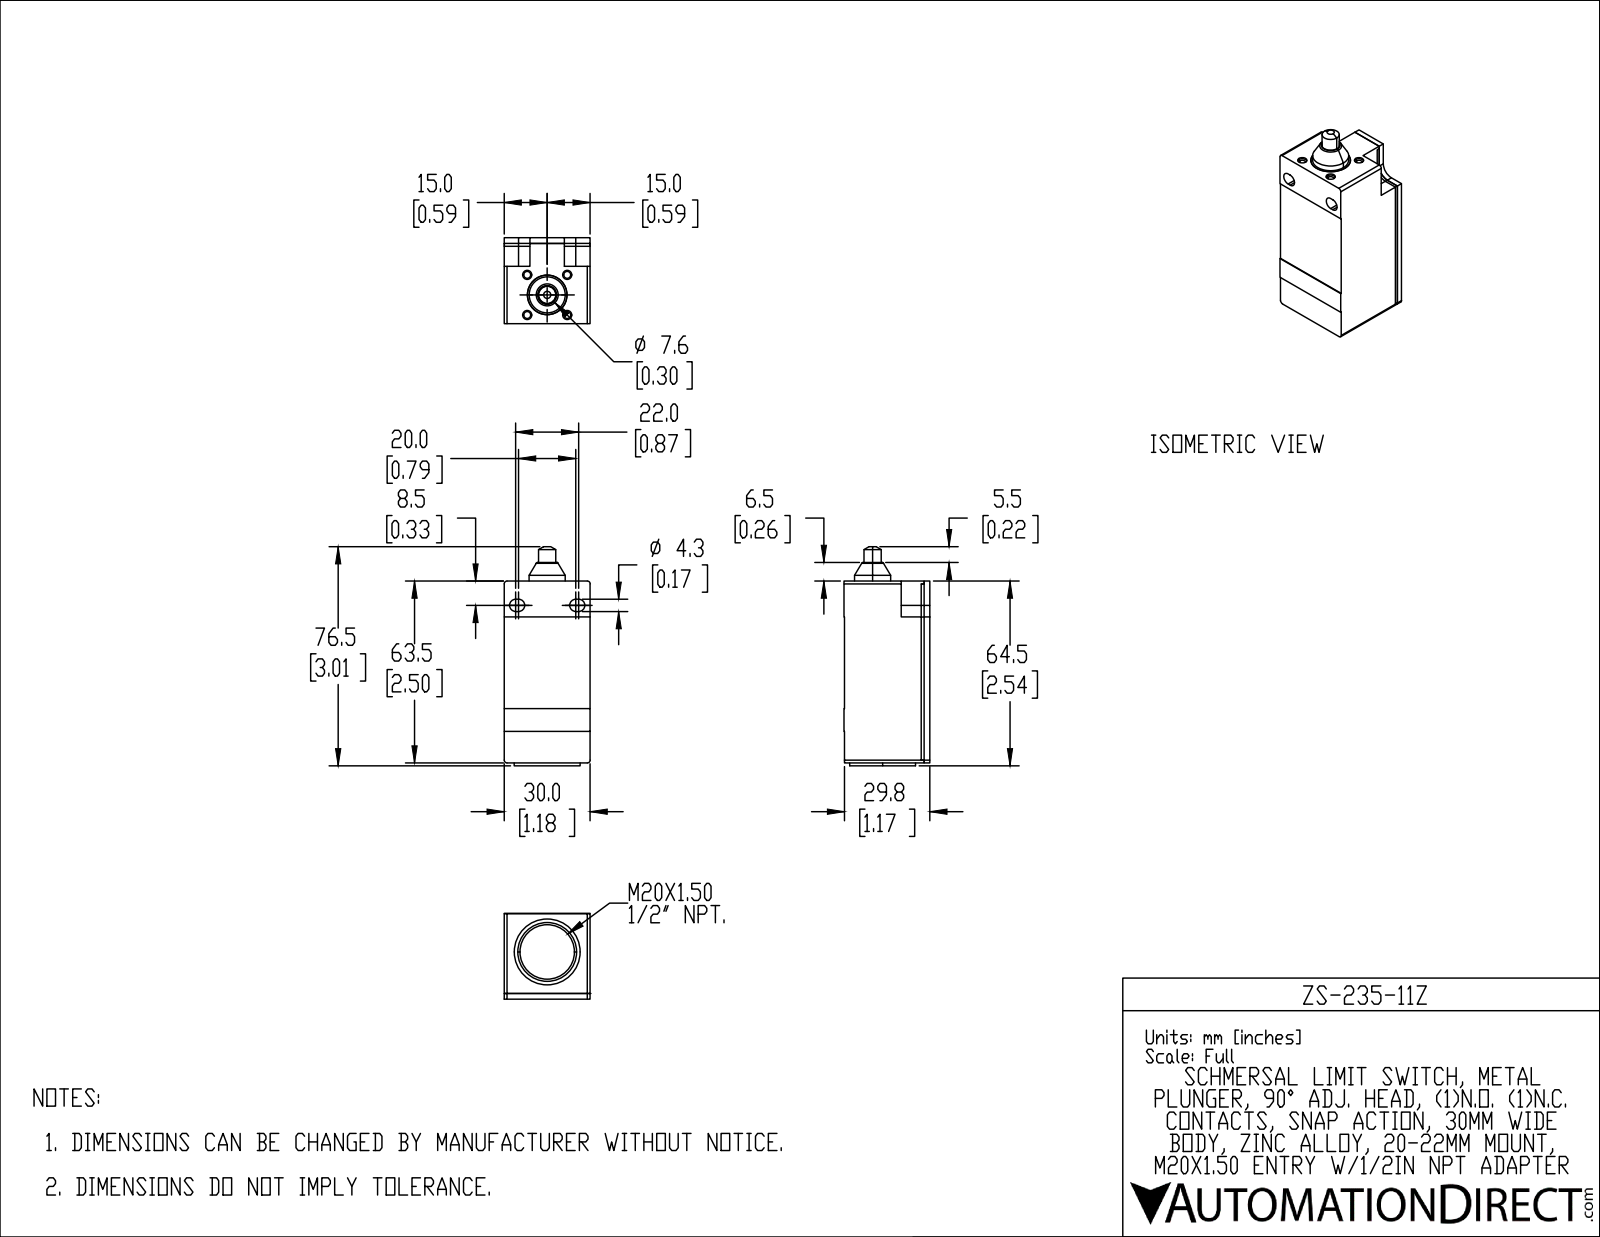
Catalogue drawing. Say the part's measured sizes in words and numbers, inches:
The part is named "ZS-235-11Z". Its 3-D file was written by "SolidWorks 2019 (AUTOMOTIVE_DESIGN)". It is 1 solid with 196 faces: 110 planar, 70 cylindrical and 16 other. Overall it measures 3.012 by 1.181 by 1.181 inches. Its volume is 3.231 cubic inches and its surface area 17.77 square inches. Round holes: 4 of diameter 0.094, 4 of diameter 0.126, 3 of diameter 0.276, 1 of diameter 0.244, 1 of diameter 0.545, 1 of diameter 0.748. Round bosses or shafts: 3 of diameter 0.256, 1 of diameter 0.906, 1 of diameter 0.543, 1 of diameter 0.496, 1 of diameter 0.236. Partial cylindrical surfaces (rounded edges, fillets, slot ends): 12 of radius 0.02, 4 of radius 0.039, 4 of radius 0.085, 2 of radius 0.157, 2 of radius 0.159. The main face-to-face distances are 1.181, 1.173, 2.5, 0.207, 2.293, 0.354, 0.039, 0.787, 0.394, 0.78. The hole center spacings are 0.39, 0.551, 0.308, 0.497, 0.78, 2.228, 0.138, 0.866.
